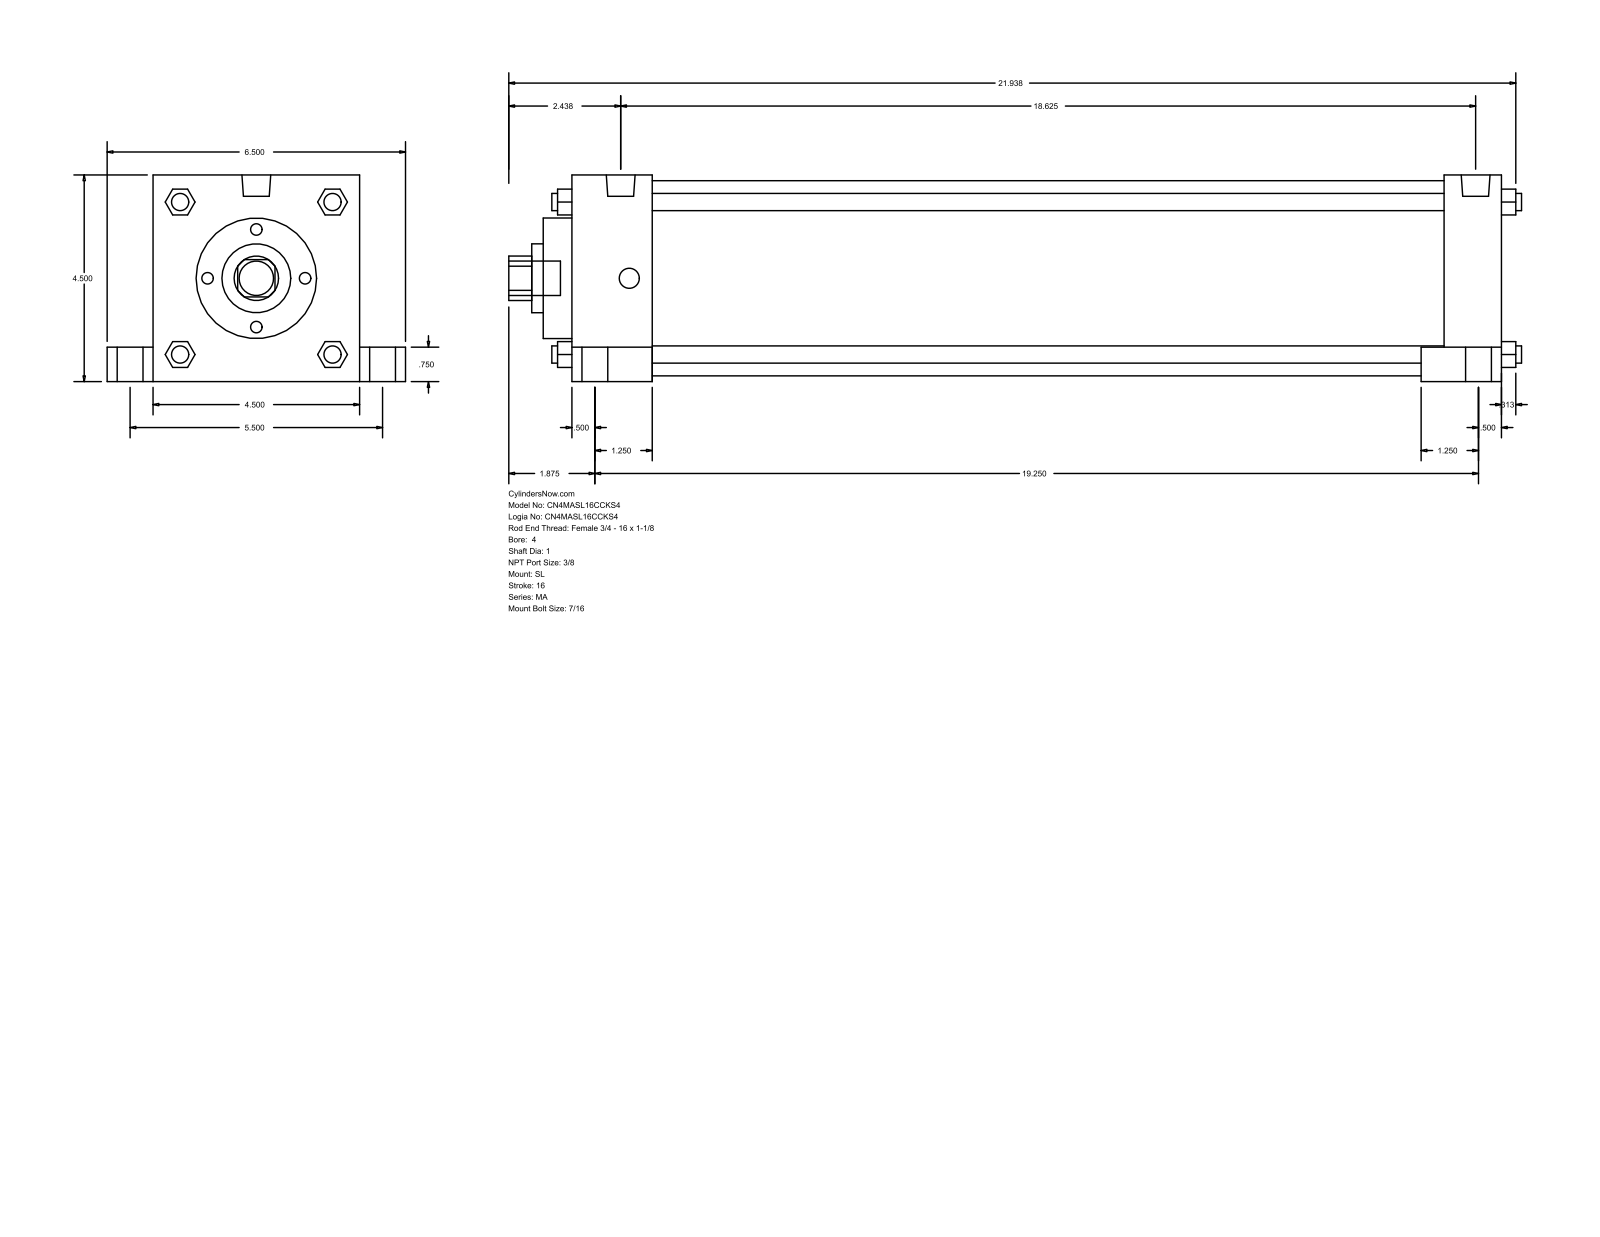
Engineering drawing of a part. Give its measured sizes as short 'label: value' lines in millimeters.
name: MA_SL__0400_1
written by: GSSL Pune (CONFIG_CONTROL_DESIGN)
unit: mm
bodies: 0 solids, 150 faces (113 planar, 37 cylindrical, 0 other)
size: 560.39 × 165.1 × 114.3
holes: 1× ⌀25.4, 1× ⌀38.1, 1× ⌀66.67, 1× ⌀107.95
bosses: 4× ⌀20.64, 4× ⌀14.29, 4× ⌀11.11, 4× ⌀9.53, 2× ⌀15.93, 1× ⌀19.05
rounds: 1× R12.29
face distances: 114.3, 514.35, 44.46, 469.89, 482.6, 438.14, 31.75, 25.4, 139.7, 530.22
